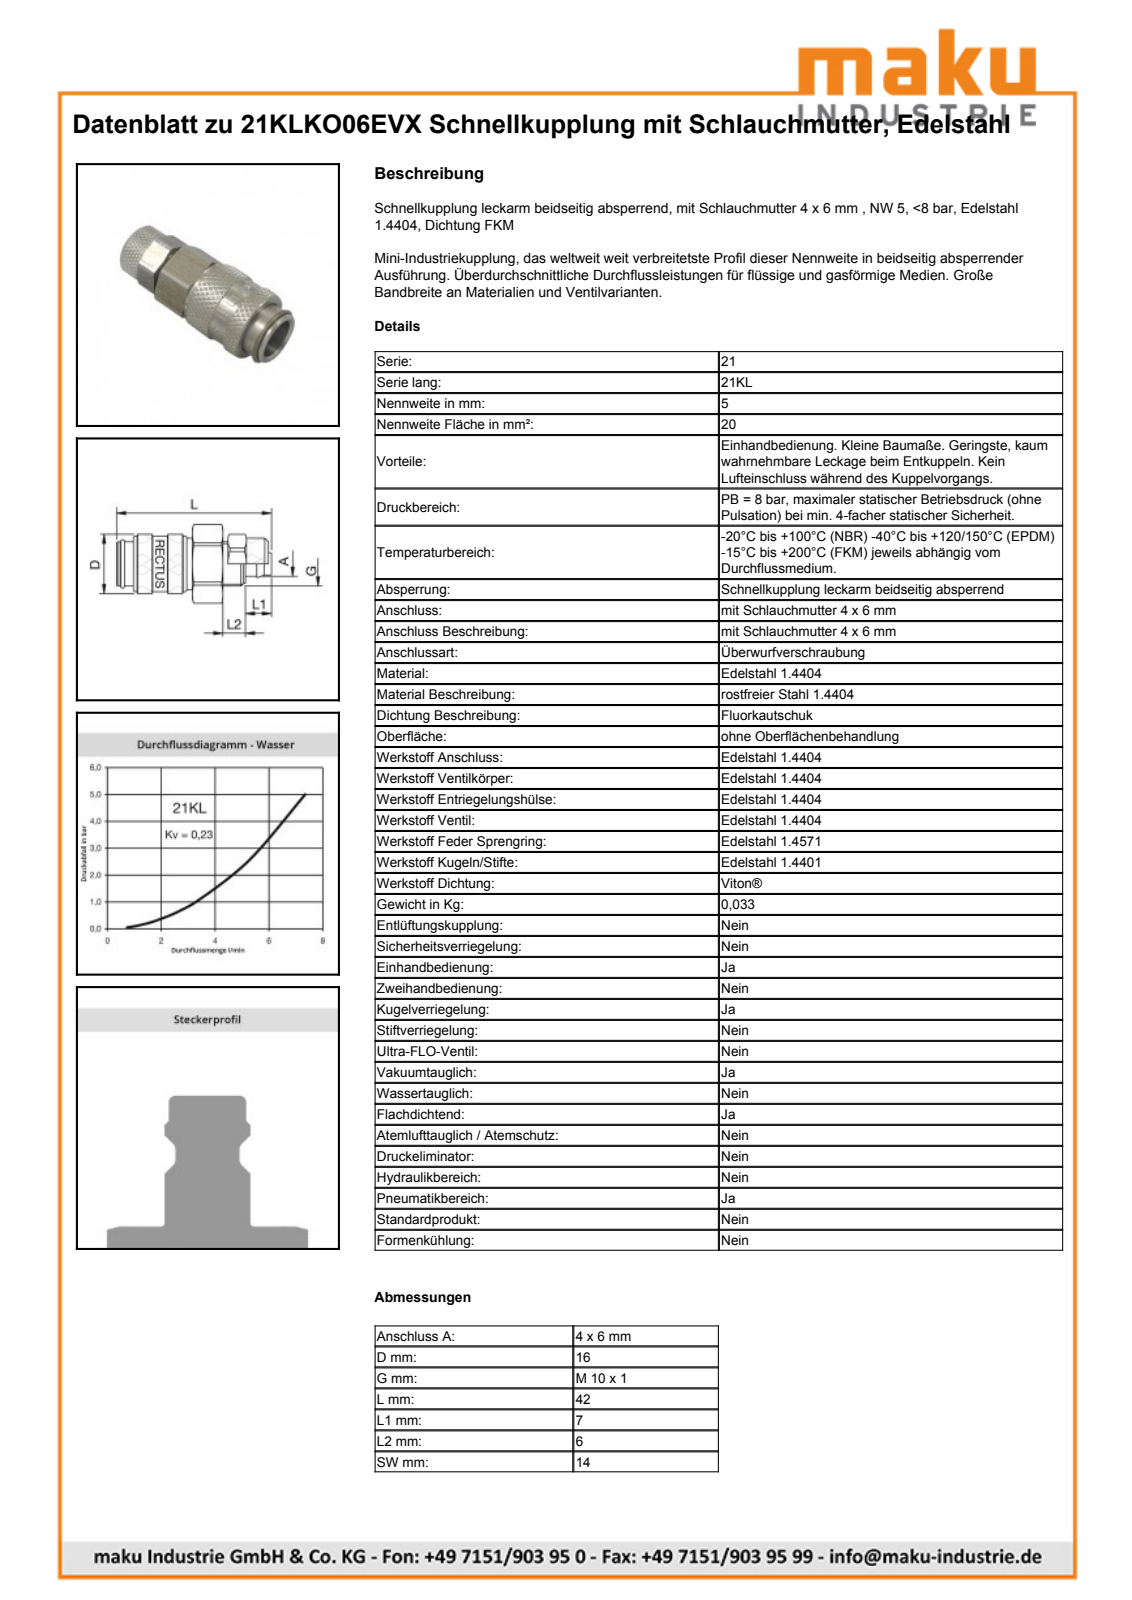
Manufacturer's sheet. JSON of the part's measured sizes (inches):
{"part_name": "D106002", "step_written_by": "Autodesk Inventor 2011 (AUTOMOTIVE_DESIGN)", "units": "inches", "bodies": {"solids": 2, "faces": 447, "planar": 140, "cylindrical": 76, "other": 231}, "overall_size": [1.654, 0.636, 0.636], "volume_in3": 0.348, "surface_area_in2": 6.589, "round_holes": [[0.244, 1], [0.394, 1], [0.413, 1], [0.421, 1], [0.478, 1], [0.551, 1]], "round_bosses_or_shafts": [[0.636, 1], [0.594, 1], [0.472, 1], [0.449, 1], [0.439, 1], [0.42, 1], [0.331, 1], [0.181, 1]], "partial_cylinders_radius": [[0.264, 1], [0.293, 1], [0.311, 1]], "face_to_face_distances": [0.551, 0.472, 1.138, 1.433, 1.614, 0.476, 1.378, 0.24, 0.236, 0.197]}
